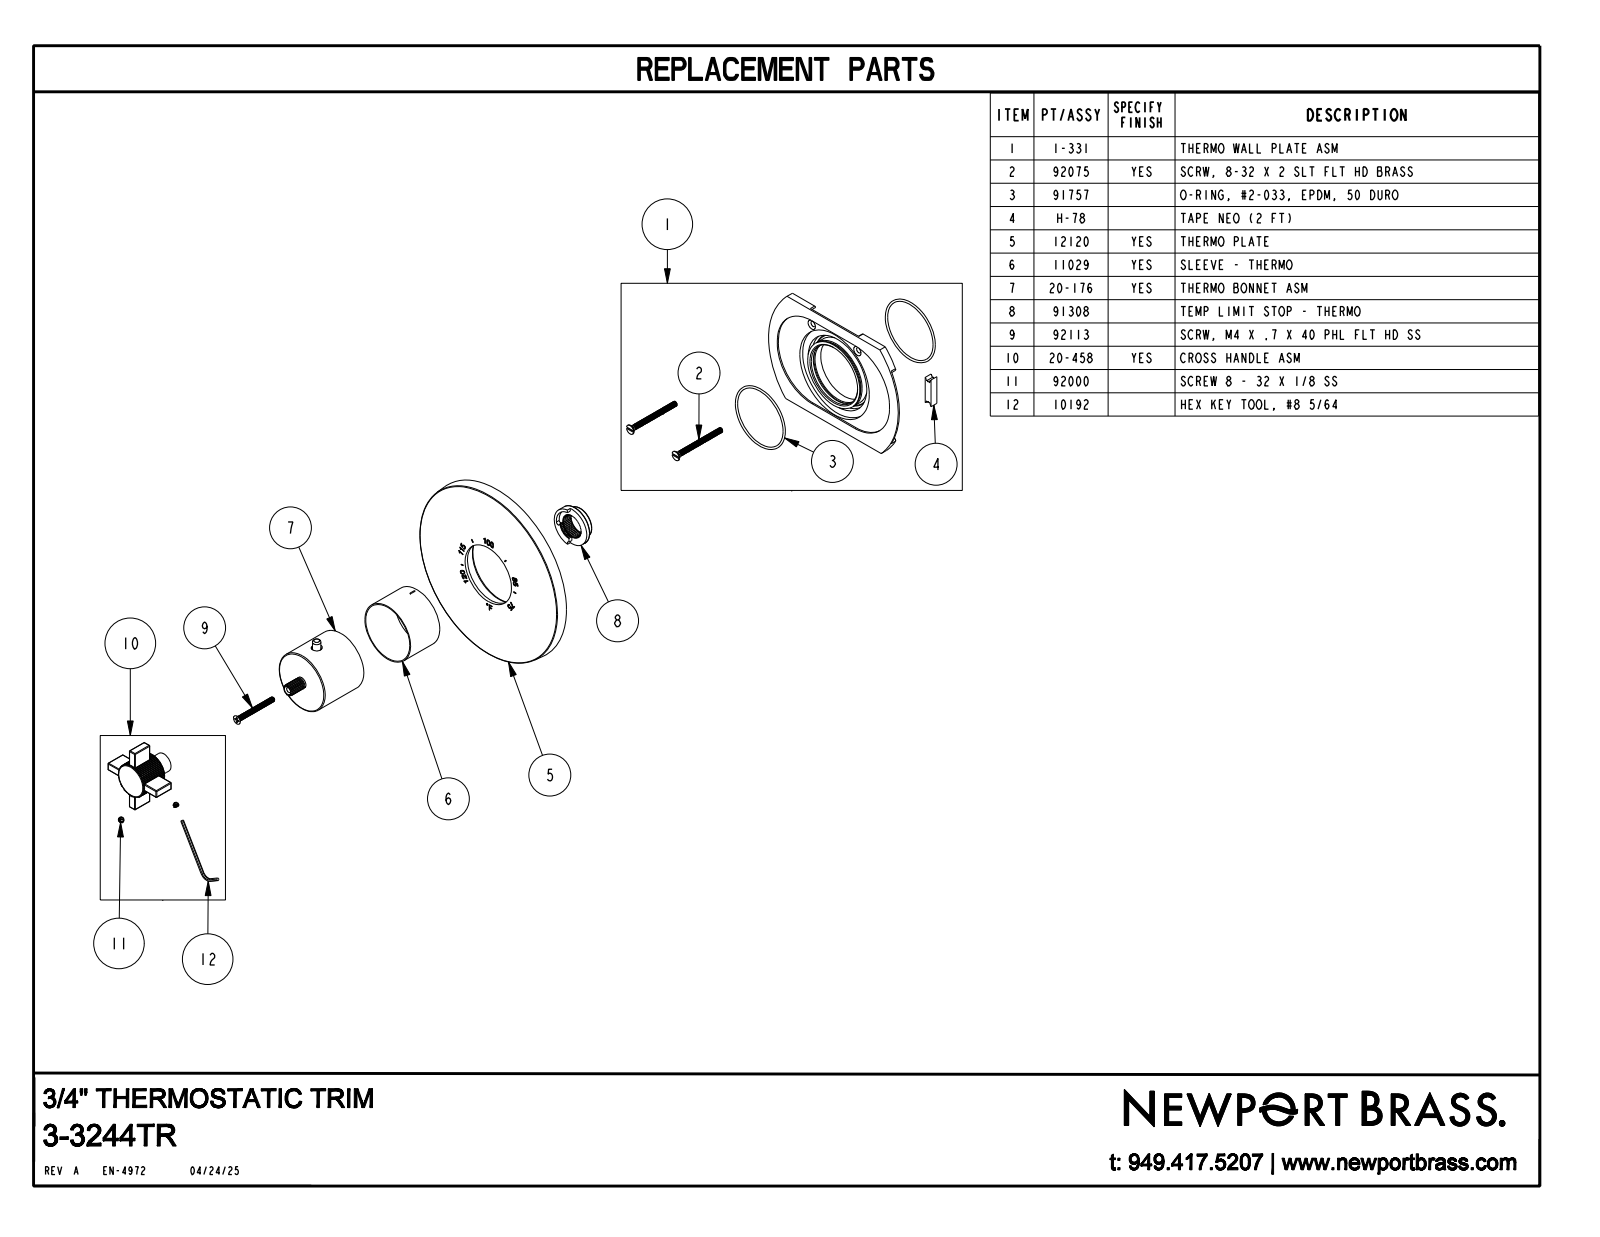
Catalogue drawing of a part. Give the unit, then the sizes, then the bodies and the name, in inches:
Units: inches
Overall size (bounding box): 6.138 × 6 × 5.994
Round holes (diameter × count): ⌀0.11 ×4, ⌀0.15 ×4, ⌀0.136 ×2, ⌀0.188 ×2, ⌀0.063 ×1, ⌀0.118 ×1, ⌀0.17 ×1, ⌀0.276 ×1, ⌀0.28 ×1, ⌀0.339 ×1, ⌀0.43 ×1, ⌀1.83 ×1
Round bosses / shafts (diameter × count): ⌀0.164 ×4, ⌀0.138 ×4, ⌀0.31 ×2, ⌀0.13 ×2, ⌀2.5 ×1, ⌀2.25 ×1, ⌀2.156 ×1, ⌀1.97 ×1
Partial cylindrical surfaces — rounded edges, fillets, slot ends (radius × count): R0.02 ×41, R0.03 ×14, R0.094 ×8, R0.1 ×8, R1.5 ×8, R0.06 ×6, R0.07 ×4, R0.098 ×4
Main face-to-face distances: 0.09, 0.05, 0.375, 0.285, 0.1, 0.185, 0.19, 0.235, 0.14, 0.125
Hole centre spacings: 0.385, 0.544, 0.74, 0.77, 1.234, 1.396, 1.5, 1.691
Volume: 8.717 in³ · Surface area: 197.3 in²
Bodies: 26 solids, 2439 faces (846 planar, 868 cylindrical, 725 other)
Part name (STEP PRODUCT): 12117; 92075; 91757; H-78_2_FEET (+8 more)
STEP written by: CREO PARAMETRIC BY PTC INC, 2023134 (CONFIG_CONTROL_DESIGN)
